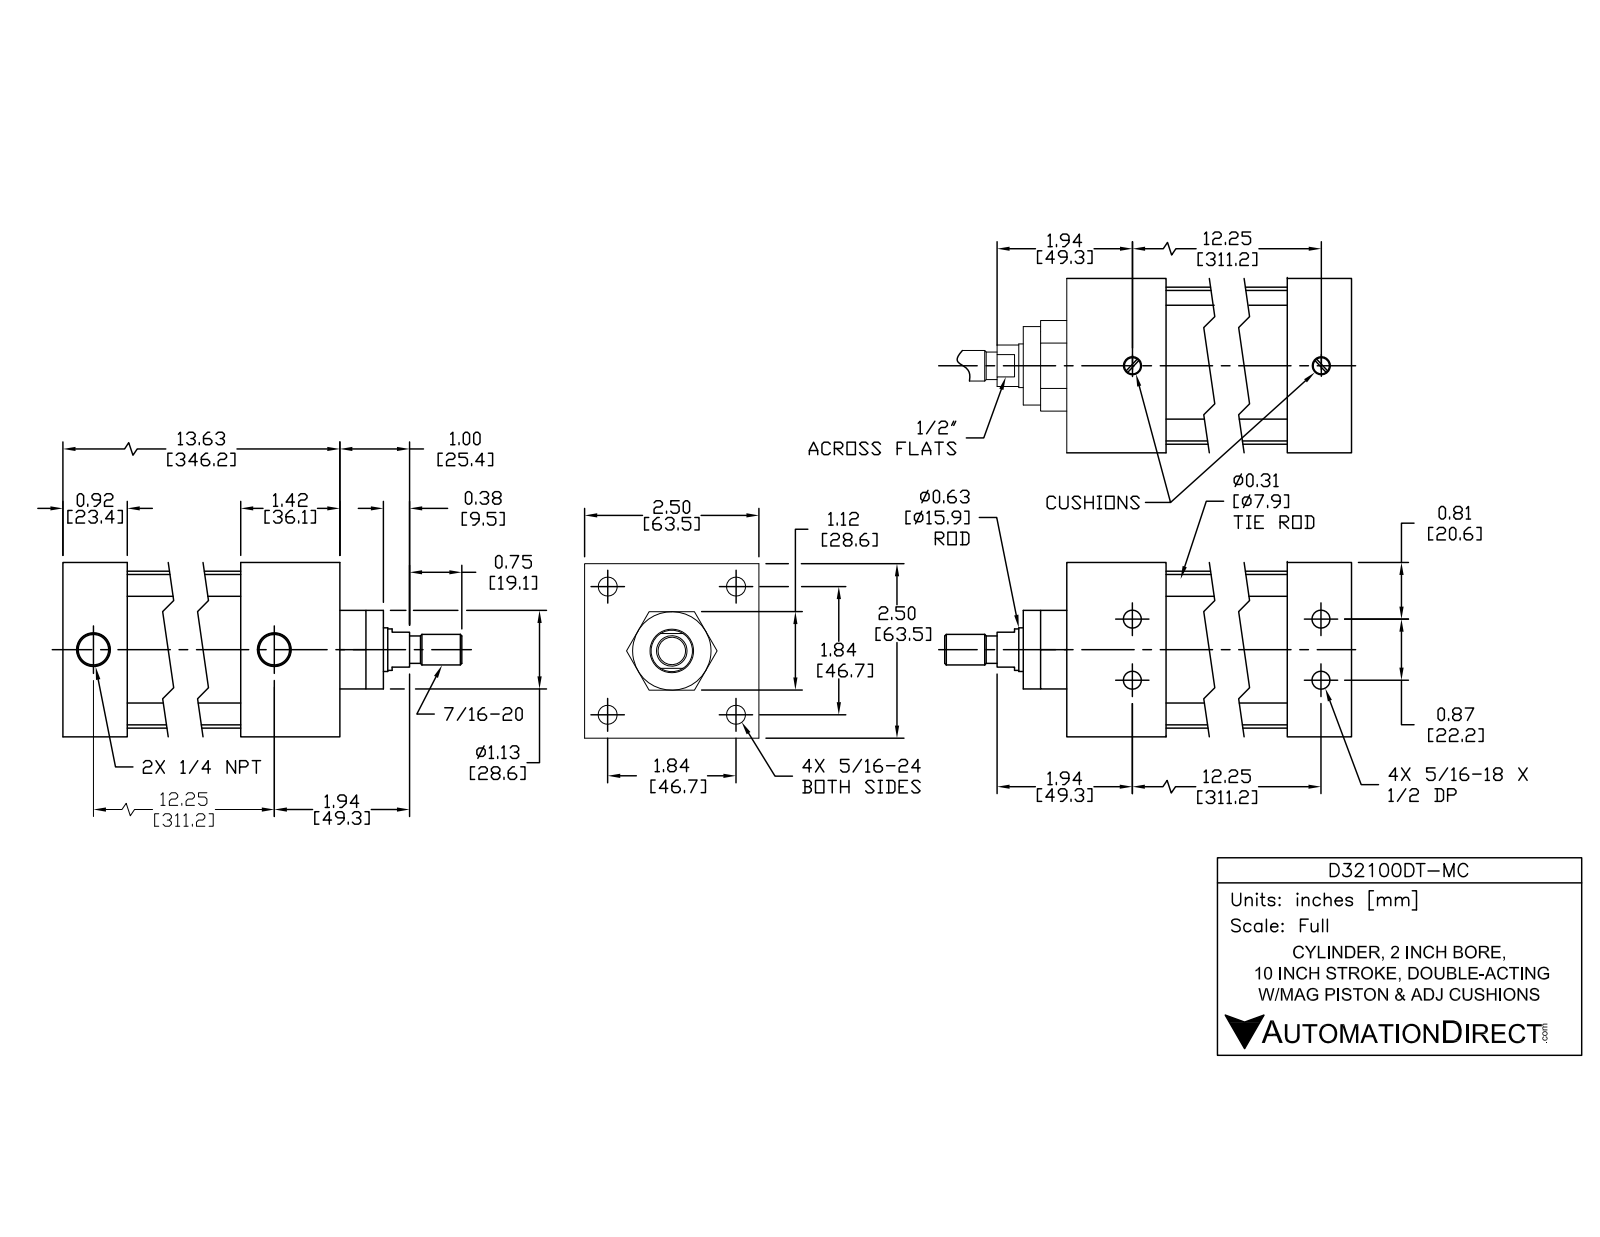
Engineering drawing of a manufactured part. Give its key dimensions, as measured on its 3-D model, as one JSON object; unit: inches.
{"part_name": "D32100DT-MC; D32100DT-M PISTON; D32100DT-M BODY", "step_written_by": "SolidWorks 2015 (AUTOMOTIVE_DESIGN)", "units": "inches", "bodies": {"solids": 12, "faces": 298, "planar": 94, "cylindrical": 114, "other": 90}, "overall_size": [15.371, 2.5, 2.5], "volume_in3": 33.72, "surface_area_in2": 312, "round_holes": [[0.252, 4], [0.267, 4], [0.359, 4], [0.5, 4], [0.297, 2], [0.477, 2], [0.625, 1], [0.628, 1], [2, 1]], "round_bosses_or_shafts": [[0.484, 4], [0.313, 4], [0.282, 4], [2.25, 1], [1.997, 1], [1.12, 1], [0.622, 1], [0.59, 1]], "partial_cylinders_radius": [[0.25, 4]], "face_to_face_distances": [2.5, 0.08, 11.201, 13.621, 1.42, 12.201, 12.701, 11.281, 0.92, 1], "hole_center_spacings": [1.307, 1.848, 12.253, 12.245, 0.437, 0.438, 0.875, 2.613]}
